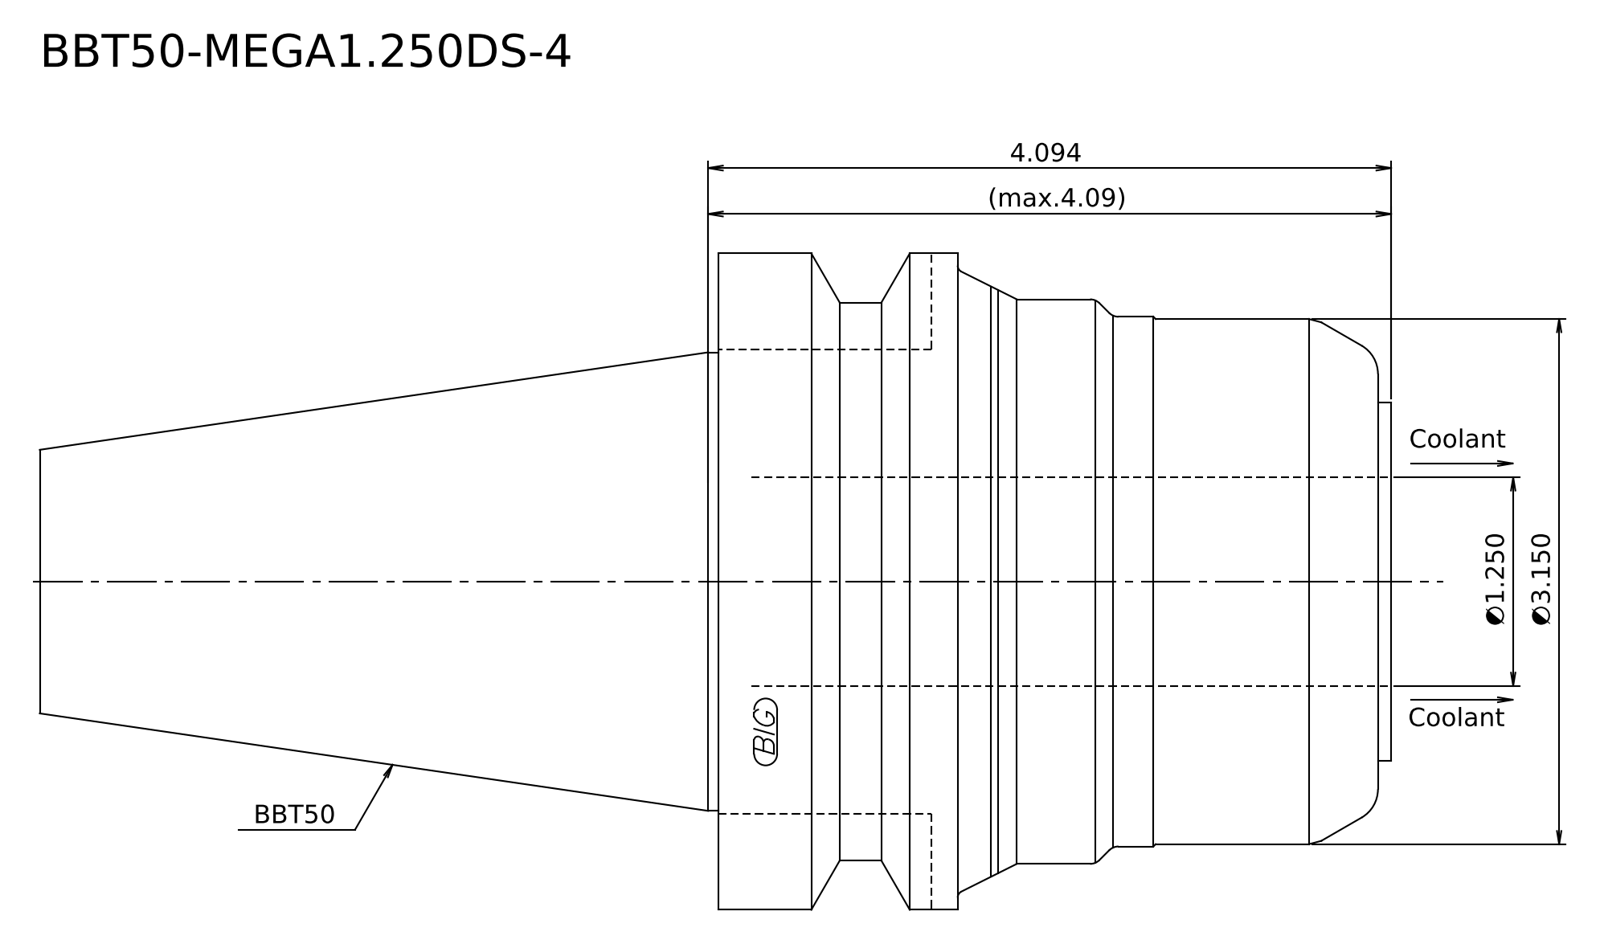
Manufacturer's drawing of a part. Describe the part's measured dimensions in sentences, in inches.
Its 3-D file was written by "Kubotek KeyCreator 2011 V10.0.2 (22737) (automotive_design)". It is 1 solid with 22 faces: 5 planar, 8 cylindrical and 9 other. Overall it measures 8.102 by 3.937 by 3.937 inches. Its volume is 52.52 cubic inches and its surface area 91.6 square inches. Round bosses or shafts: 1 of diameter 3.937, 1 of diameter 3.386, 1 of diameter 3.346, 1 of diameter 3.177, 1 of diameter 3.15, 1 of diameter 2.75, 1 of diameter 2.152. The main face-to-face distances are 4.035, 0.079, 3.957, 8.102, 8.024, 4.067, 2.598, 2.52, 1.437, 5.504.
